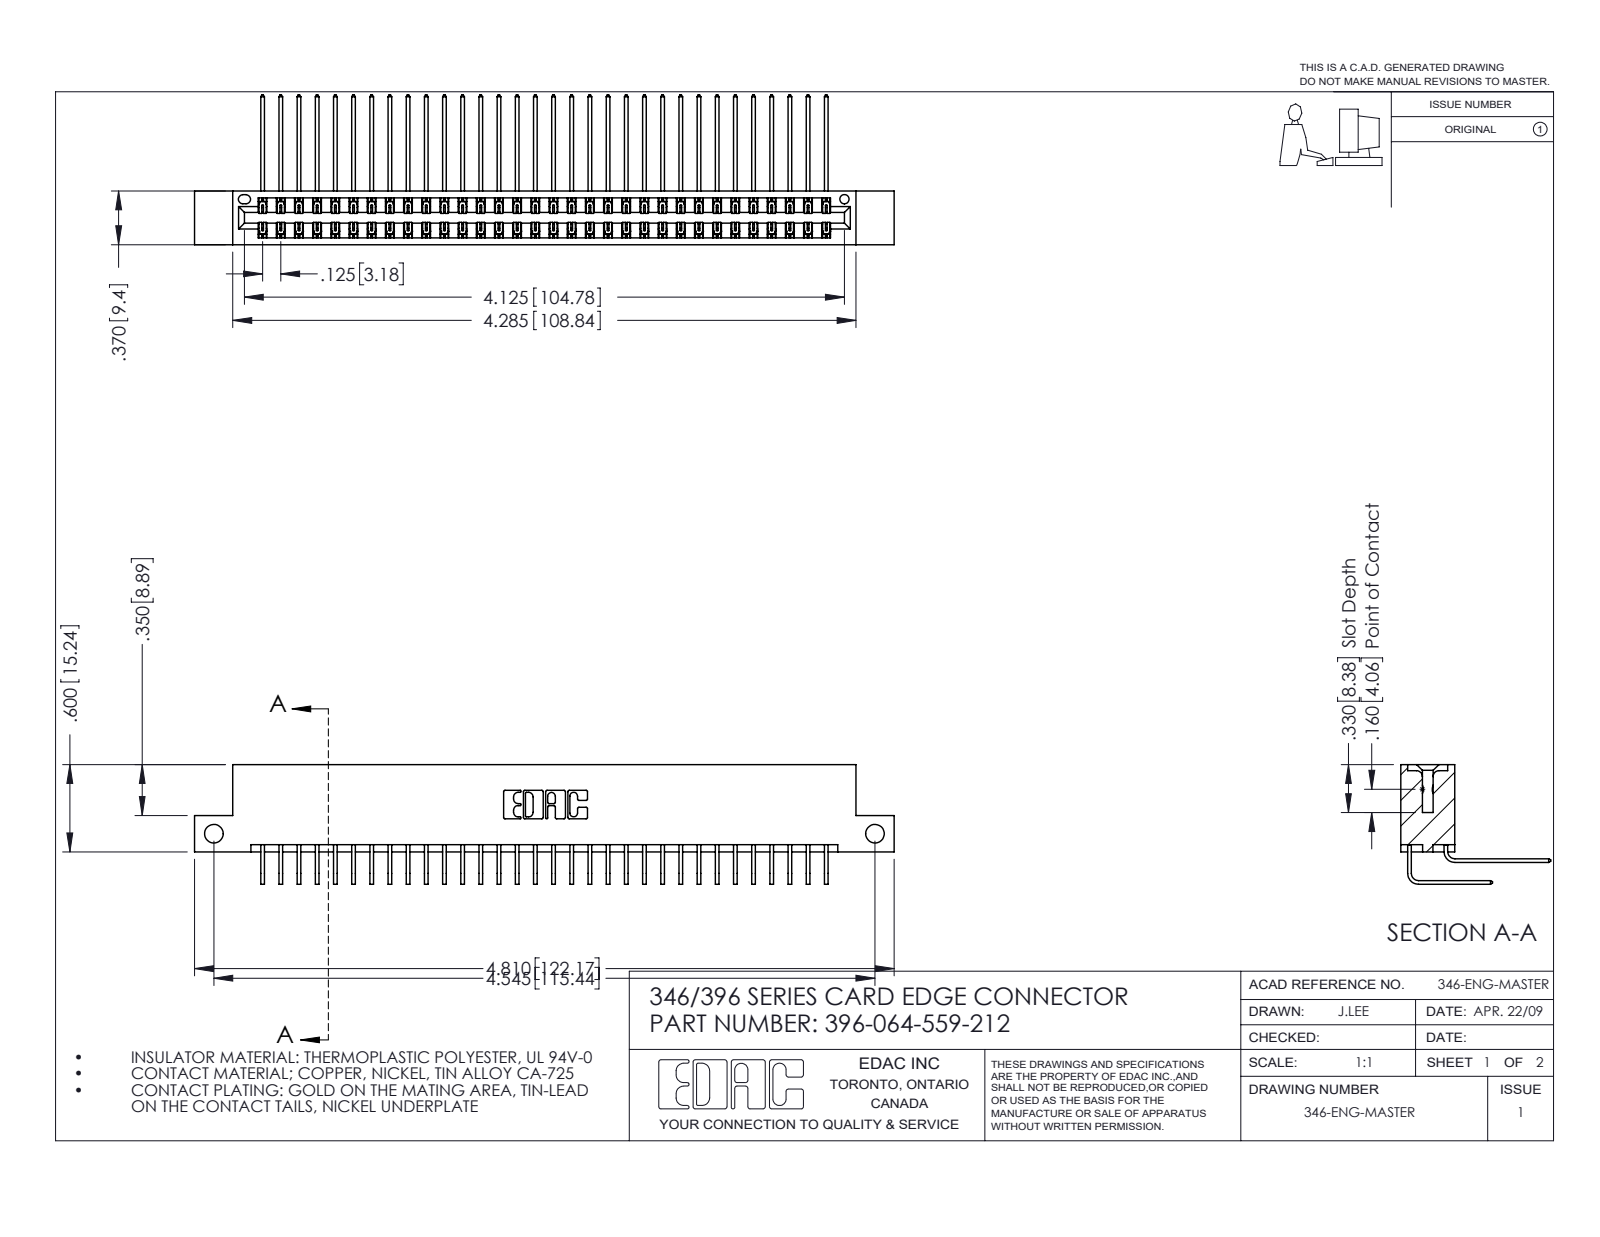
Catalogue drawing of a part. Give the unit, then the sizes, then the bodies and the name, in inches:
Units: inches
Overall size (bounding box): 4.81 × 1.03 × 0.823
Round holes (diameter × count): ⌀0.128 ×2, ⌀0.064 ×1
Partial cylindrical surfaces — rounded edges, fillets, slot ends (radius × count): R0.006 ×96, R0.01 ×22, R0.007 ×6, R0.031 ×6, R0.026 ×3, R0.014 ×2, R0.022 ×2, R0.024 ×2
Main face-to-face distances: 0.048, 0.322, 0.025, 0.25, 0.37, 0.072, 0.298, 0.275, 0.148, 0.222
Hole centre spacings: 4.545
Volume: 0.739 in³ · Surface area: 28.11 in²
Bodies: 65 solids, 3578 faces (2444 planar, 1134 cylindrical, 0 other)
Part name (STEP PRODUCT): 345-292-001_559 Tail - 2; 396-064-559-212; 345-292-001_558 559 Tail - 1; 346 Part_Flush Mounting Lugs - Side Mount
STEP written by: SolidWorks 2016 (CONFIG_CONTROL_DESIGN)
